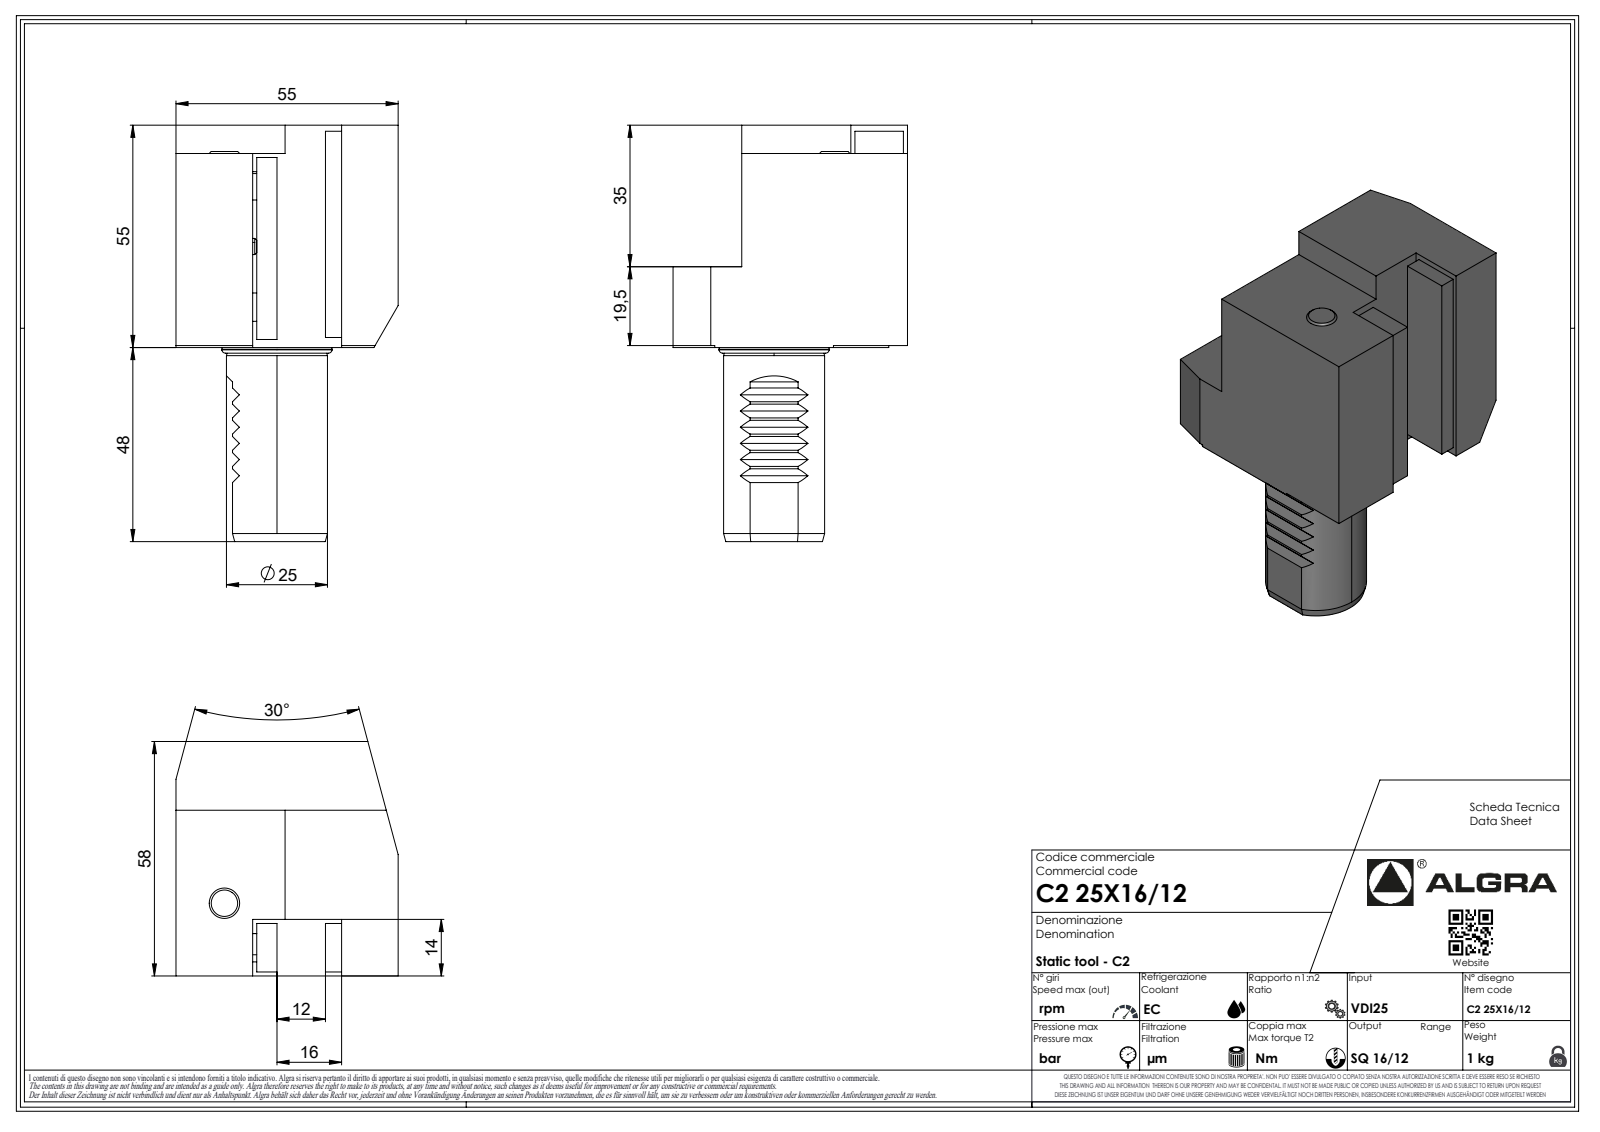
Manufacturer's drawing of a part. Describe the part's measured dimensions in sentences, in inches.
The part is named "C225X1612". Its 3-D file was written by "SolidWorks 2023 (AUTOMOTIVE_DESIGN)". It is 1 solid with 303 faces: 213 planar, 35 cylindrical and 55 other. Overall it measures 4.055 by 2.283 by 2.165 inches. Its volume is 8.709 cubic inches and its surface area 36.03 square inches. Round holes: 1 of diameter 0.083. Round bosses or shafts: 2 of diameter 0.276, 1 of diameter 1.081, 1 of diameter 0.984, 1 of diameter 0.251, 1 of diameter 0.157, 1 of diameter 0.067. Partial cylindrical surfaces (rounded edges, fillets, slot ends): 7 of radius 0.013, 7 of radius 0.02, 7 of radius 0.146, 1 of radius 0.008, 1 of radius 1.142. The main face-to-face distances are 2.165, 1.614, 0.551, 1.063, 1.102, 1.89, 0.039, 0.669, 1.378, 0.787.
